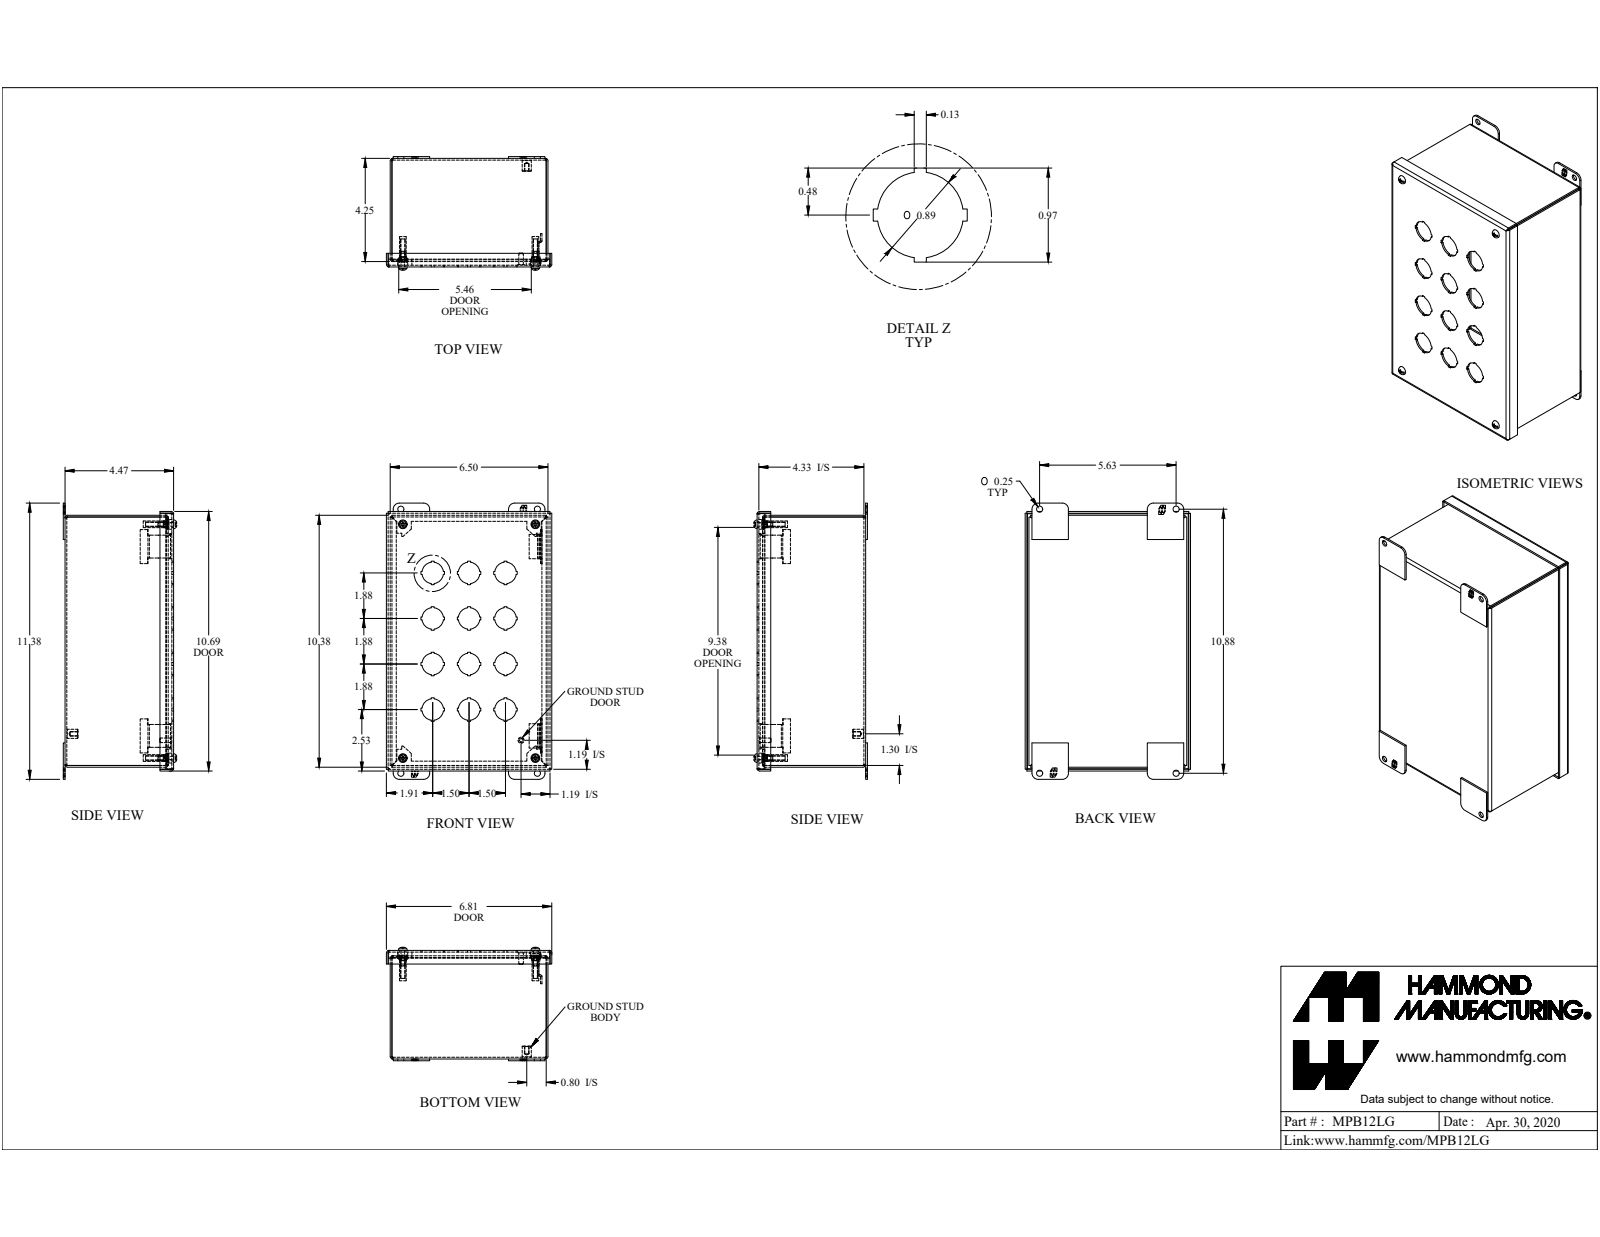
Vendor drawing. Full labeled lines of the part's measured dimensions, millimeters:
Part name (STEP PRODUCT): MPB12LG
STEP written by: SolidWorks 2019 (AUTOMOTIVE_DESIGN)
Units: millimetres
Bodies: 23 solids, 843 faces (643 planar, 164 cylindrical, 36 other)
Overall size (bounding box): 288.9 × 173.1 × 118.6
Volume: 414 900 mm³ · Surface area: 436 100 mm²
Round holes (diameter × count): ⌀22.5 ×12, ⌀6.4 ×8, ⌀4 ×4, ⌀10.3 ×4, ⌀4 ×1
Round bosses / shafts (diameter × count): ⌀9.9 ×4, ⌀7 ×4, ⌀4.8 ×4, ⌀3.8 ×4, ⌀9.5 ×1, ⌀6.4 ×1, ⌀4.8 ×1
Partial cylindrical surfaces — rounded edges, fillets, slot ends (radius × count): R0.9 ×12, R2.7 ×12, R6.4 ×8, R0.7 ×4, R2.2 ×4, R4.1 ×4, R4.3 ×4
Main face-to-face distances: 1.8, 111.8, 163.3, 113.6, 109.9, 261.7, 165.1, 161.4, 263.5, 259.9
Hole centre spacings: 61, 38.1, 102.6, 138.7, 141.7, 47.6, 89.9, 95.3
